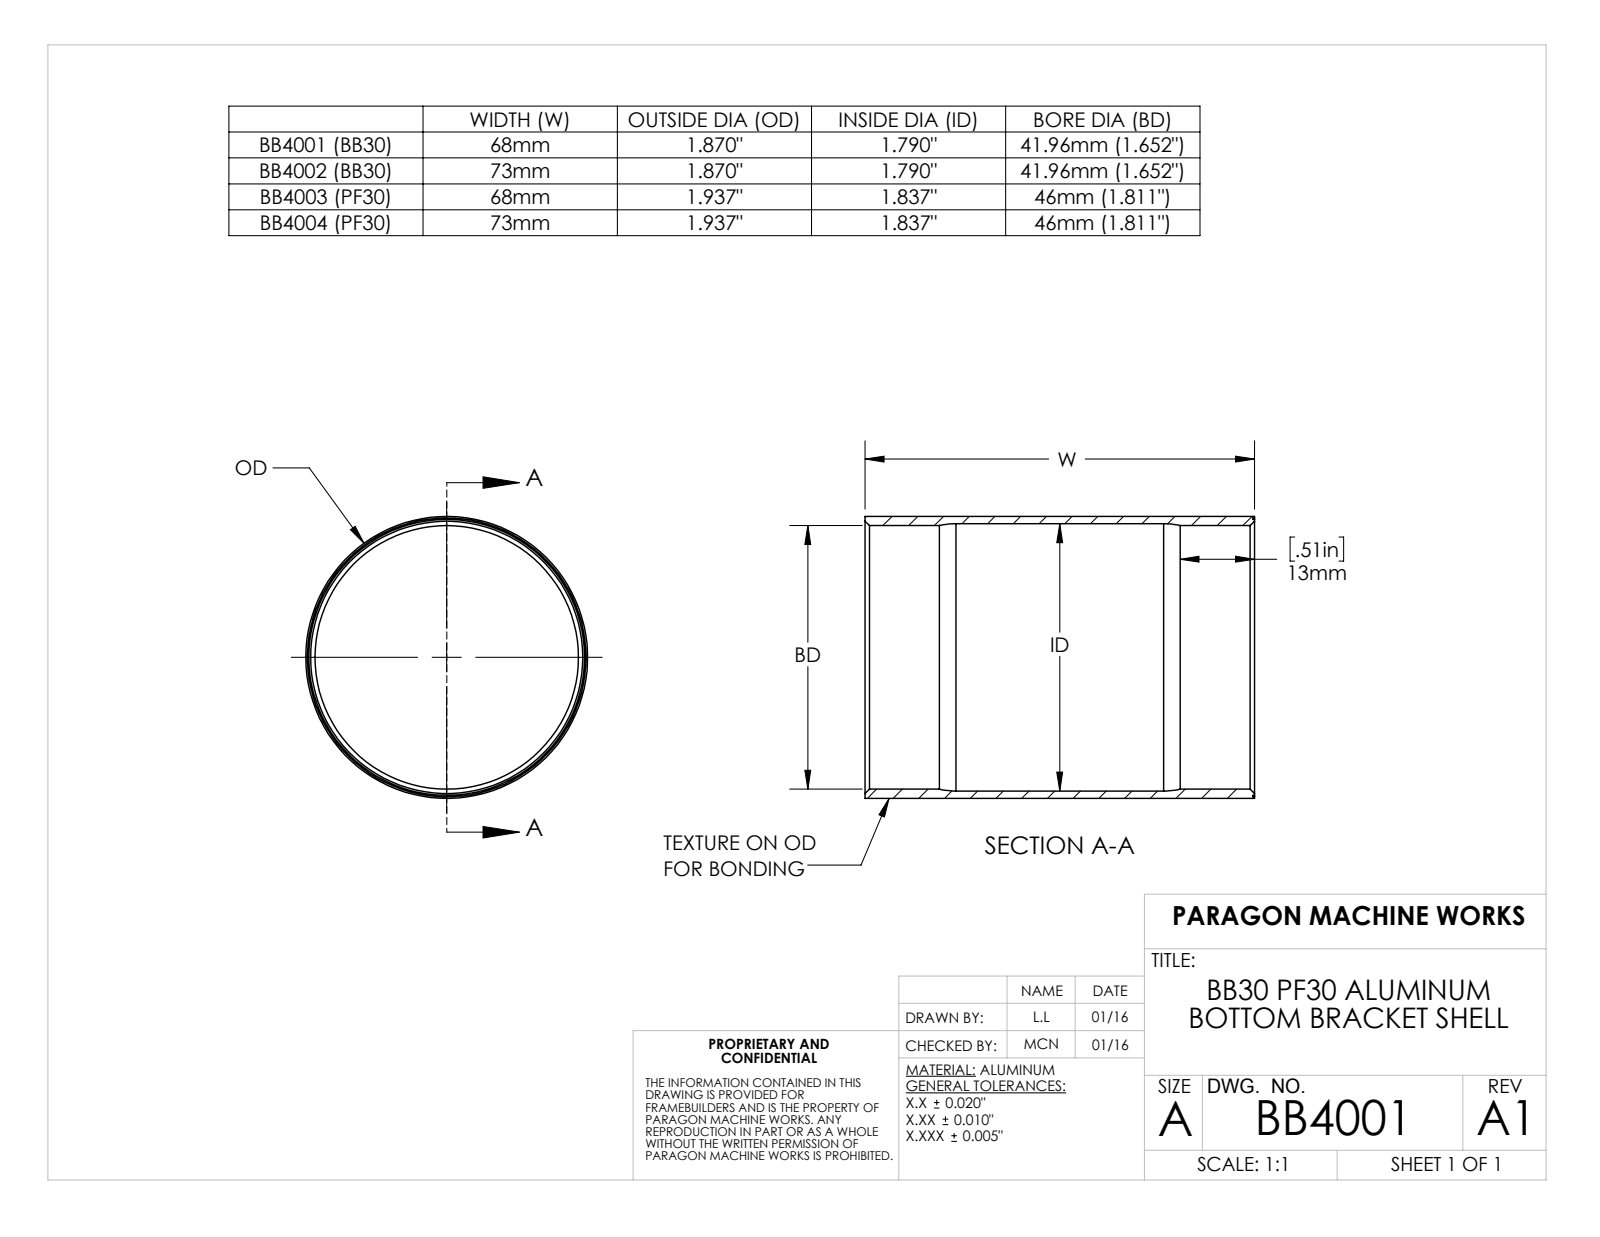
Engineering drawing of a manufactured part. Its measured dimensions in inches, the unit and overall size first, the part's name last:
Units: inches
Overall size (bounding box): 2.677 × 1.937 × 1.937
Round holes (diameter × count): ⌀1.811 ×1, ⌀1.837 ×1, ⌀1.916 ×1
Round bosses / shafts (diameter × count): ⌀1.937 ×1, ⌀1.896 ×1
Main face-to-face distances: 2.677, 2.667
Volume: 0.874 in³ · Surface area: 32.33 in²
Bodies: 1 solid, 24 faces (4 planar, 12 cylindrical, 8 other)
Part name (STEP PRODUCT): BB4001
STEP written by: SolidWorks 2016 (AUTOMOTIVE_DESIGN)
